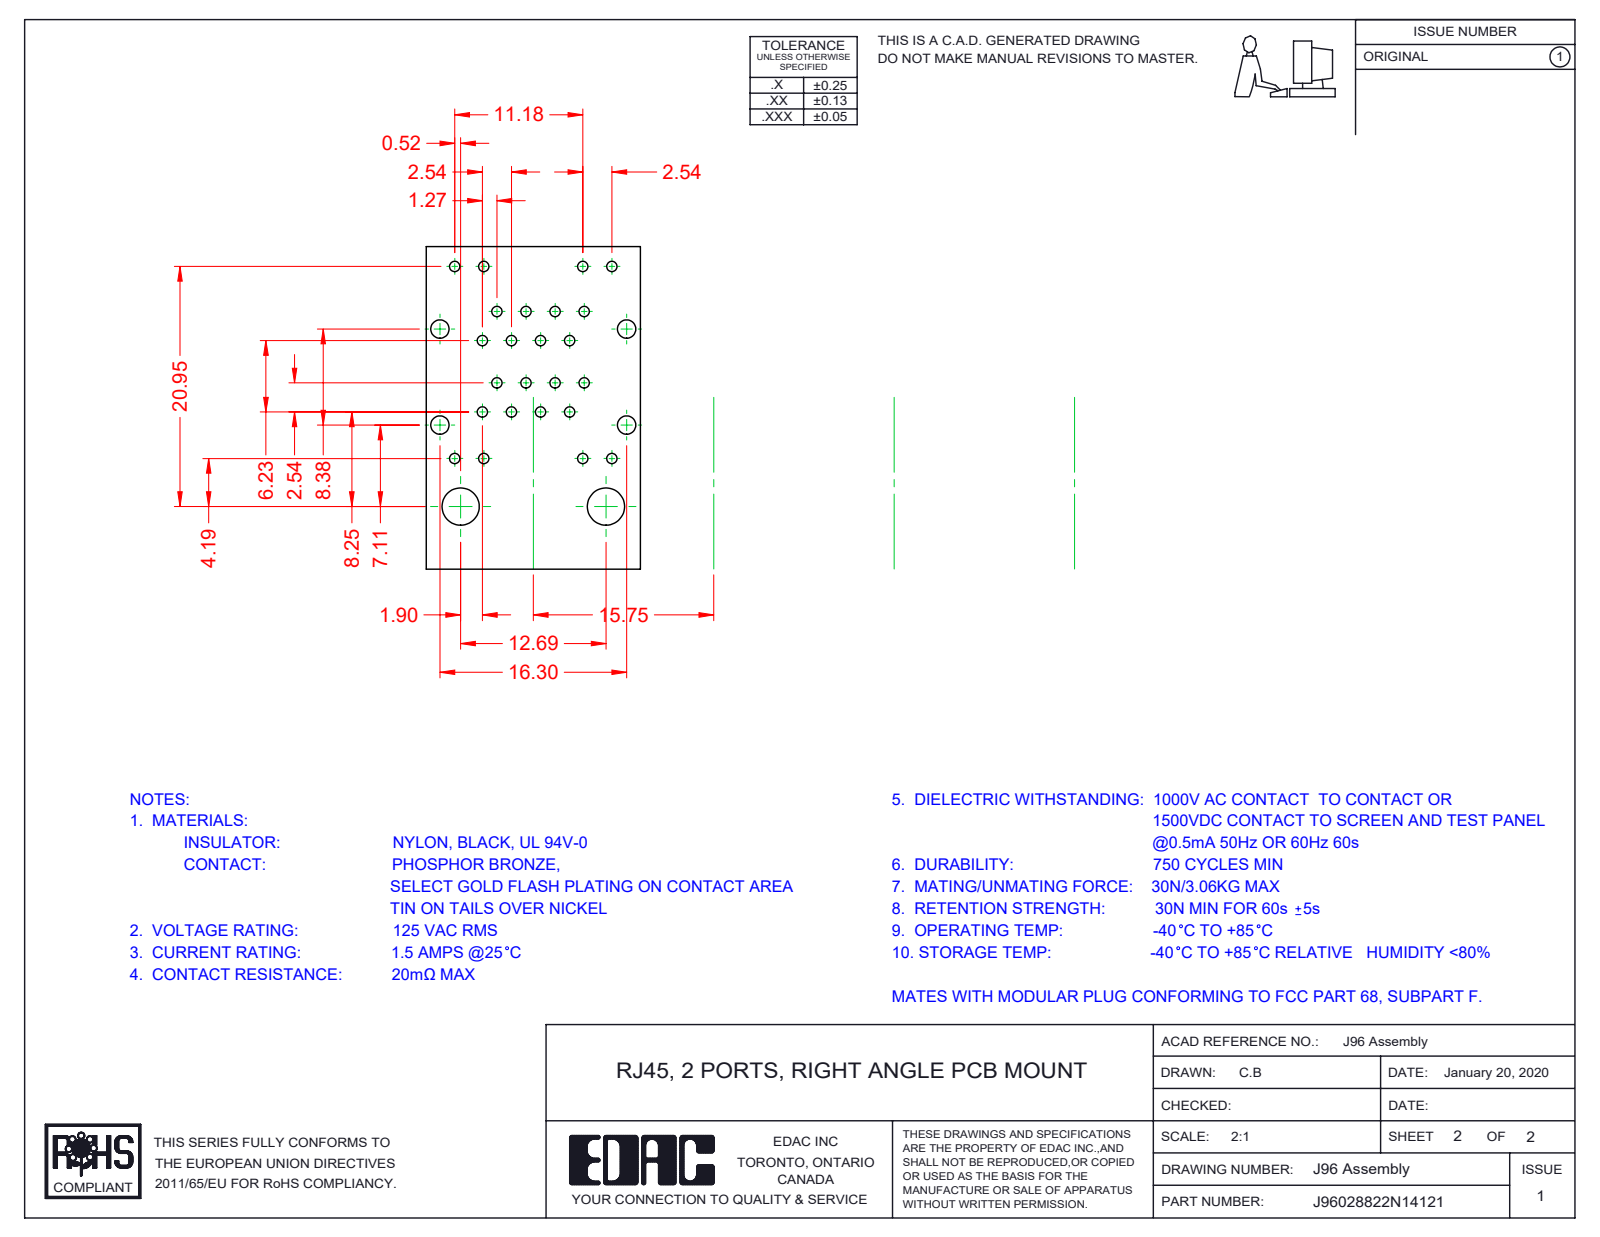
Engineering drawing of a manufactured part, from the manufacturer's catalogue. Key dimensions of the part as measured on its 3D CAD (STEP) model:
Part name (STEP PRODUCT): 96 Shield_2 Ports LED - No EMI; 96 Contact Lock Lower; 96 Insulator Insert; 96 Contact Lock Upper (+8 more)
STEP written by: SolidWorks 2016 (CONFIG_CONTROL_DESIGN)
Units: millimetres
Bodies: 27 solids, 2382 faces (1849 planar, 427 cylindrical, 106 other)
Overall size (bounding box): 29.58 × 28.68 × 16.8
Volume: 6 852 mm³ · Surface area: 19 109 mm²
Partial cylindrical surfaces — rounded edges, fillets, slot ends (radius × count): R0.25 ×48, R0.15 ×32, R0.35 ×24, R0.5 ×16, R1 ×16, R0.2 ×13, R0.7 ×9, R2 ×5
Main face-to-face distances: 16.3, 16.1, 1.75, 16.5, 14.75, 1.55, 14.55, 0.53, 1.48, 11.2
